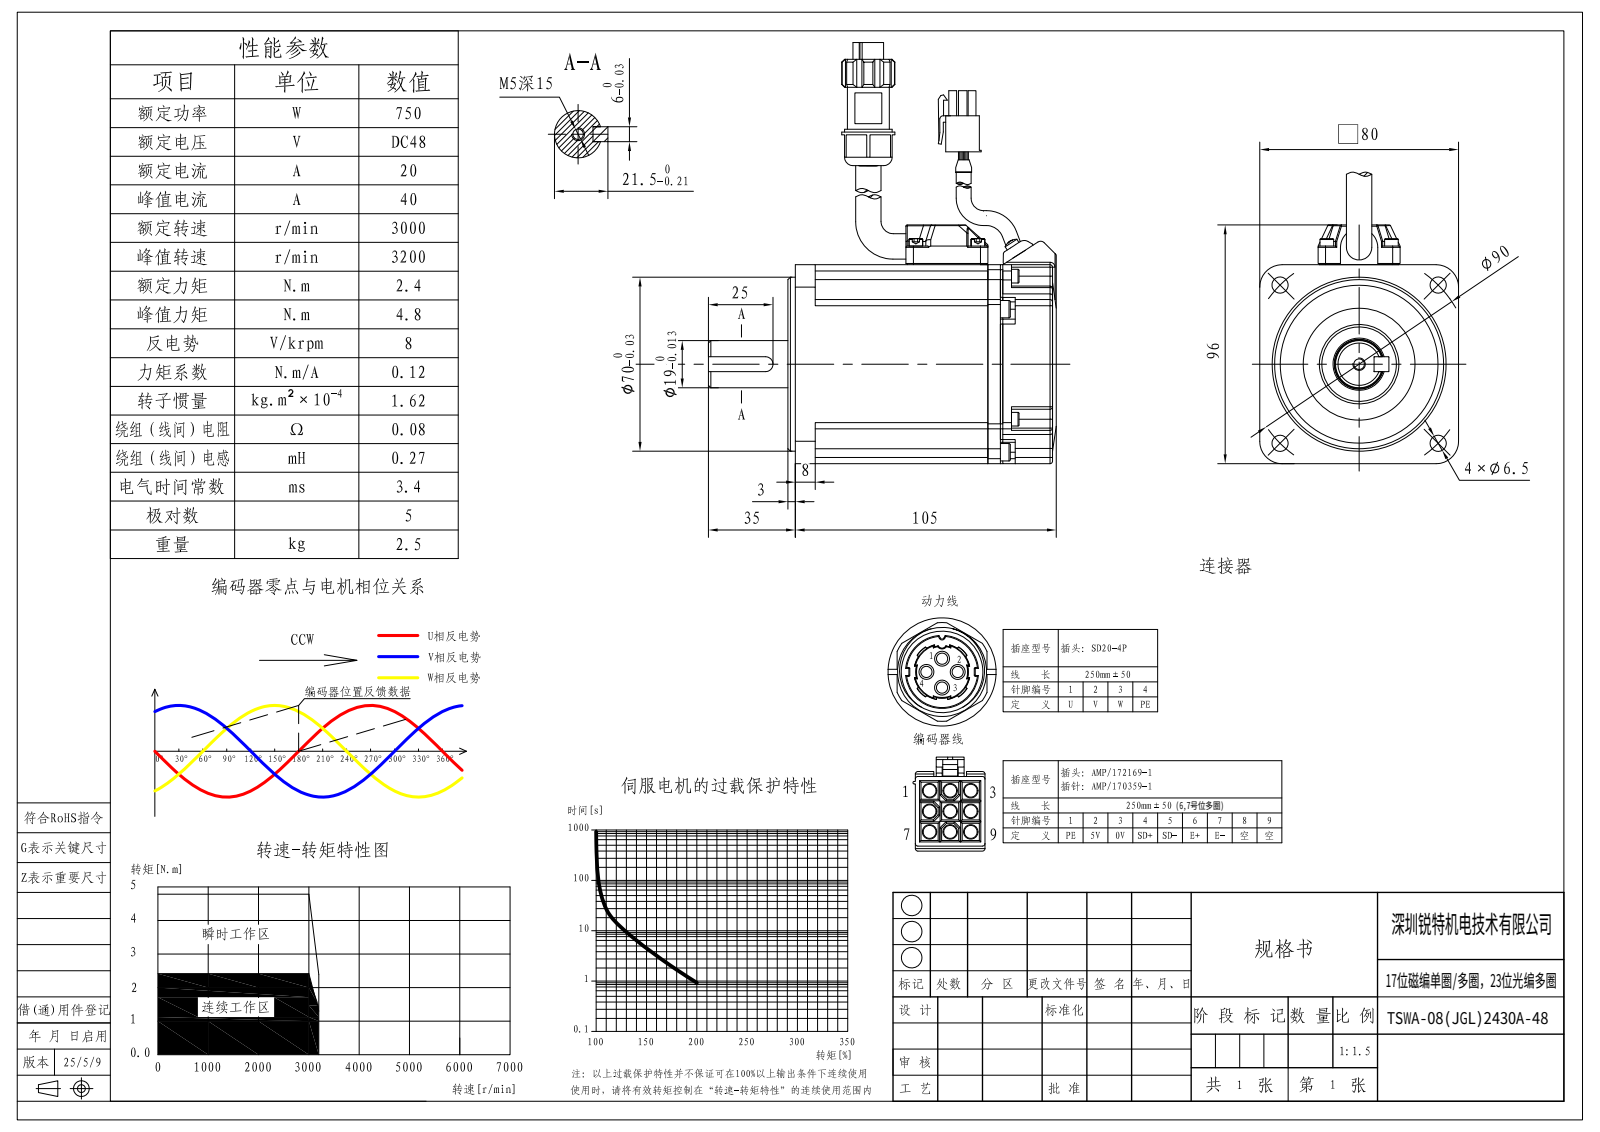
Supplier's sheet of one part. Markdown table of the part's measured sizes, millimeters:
| quantity | value |
| --- | --- |
| STEP written by | SolidWorks 2018 (CONFIG_CONTROL_DESIGN) |
| units | millimeters |
| bodies | 7 solids, 918 faces (390 planar, 374 cylindrical, 154 other) |
| overall size | 140 × 93.5 × 80 |
| volume | 616 838 mm³ |
| surface area | 83 827 mm² |
| round holes (diameter × count) | 3.3 × 10, 2.5 × 5, 4.2 × 5, 2 × 4, 3.5 × 4, 6.5 × 4, 6 × 1, 6.3 × 1, 7.6 × 1, 8 × 1, 10 × 1, 11.8 × 1 |
| round bosses / shafts (diameter × count) | 4 × 6, 7 × 4, 5.5 × 4, 3 × 4, 2.2 × 2, 77.5 × 1, 74.7 × 1, 70 × 1 |
| partial cylindrical surfaces (radius × count) | 1 × 37, 2 × 29, 0.5 × 13, 8 × 12, 0.6 × 9, 2.5 × 8, 4 × 8, 3 × 5 |
| main face-to-face distances | 80, 3, 77.5, 0.5, 101.5, 24, 1, 27.5, 2.5, 14 |
| hole center spacings | 8, 59.04, 86.19, 10.33, 10.34, 16, 18.78, 41.75 |
